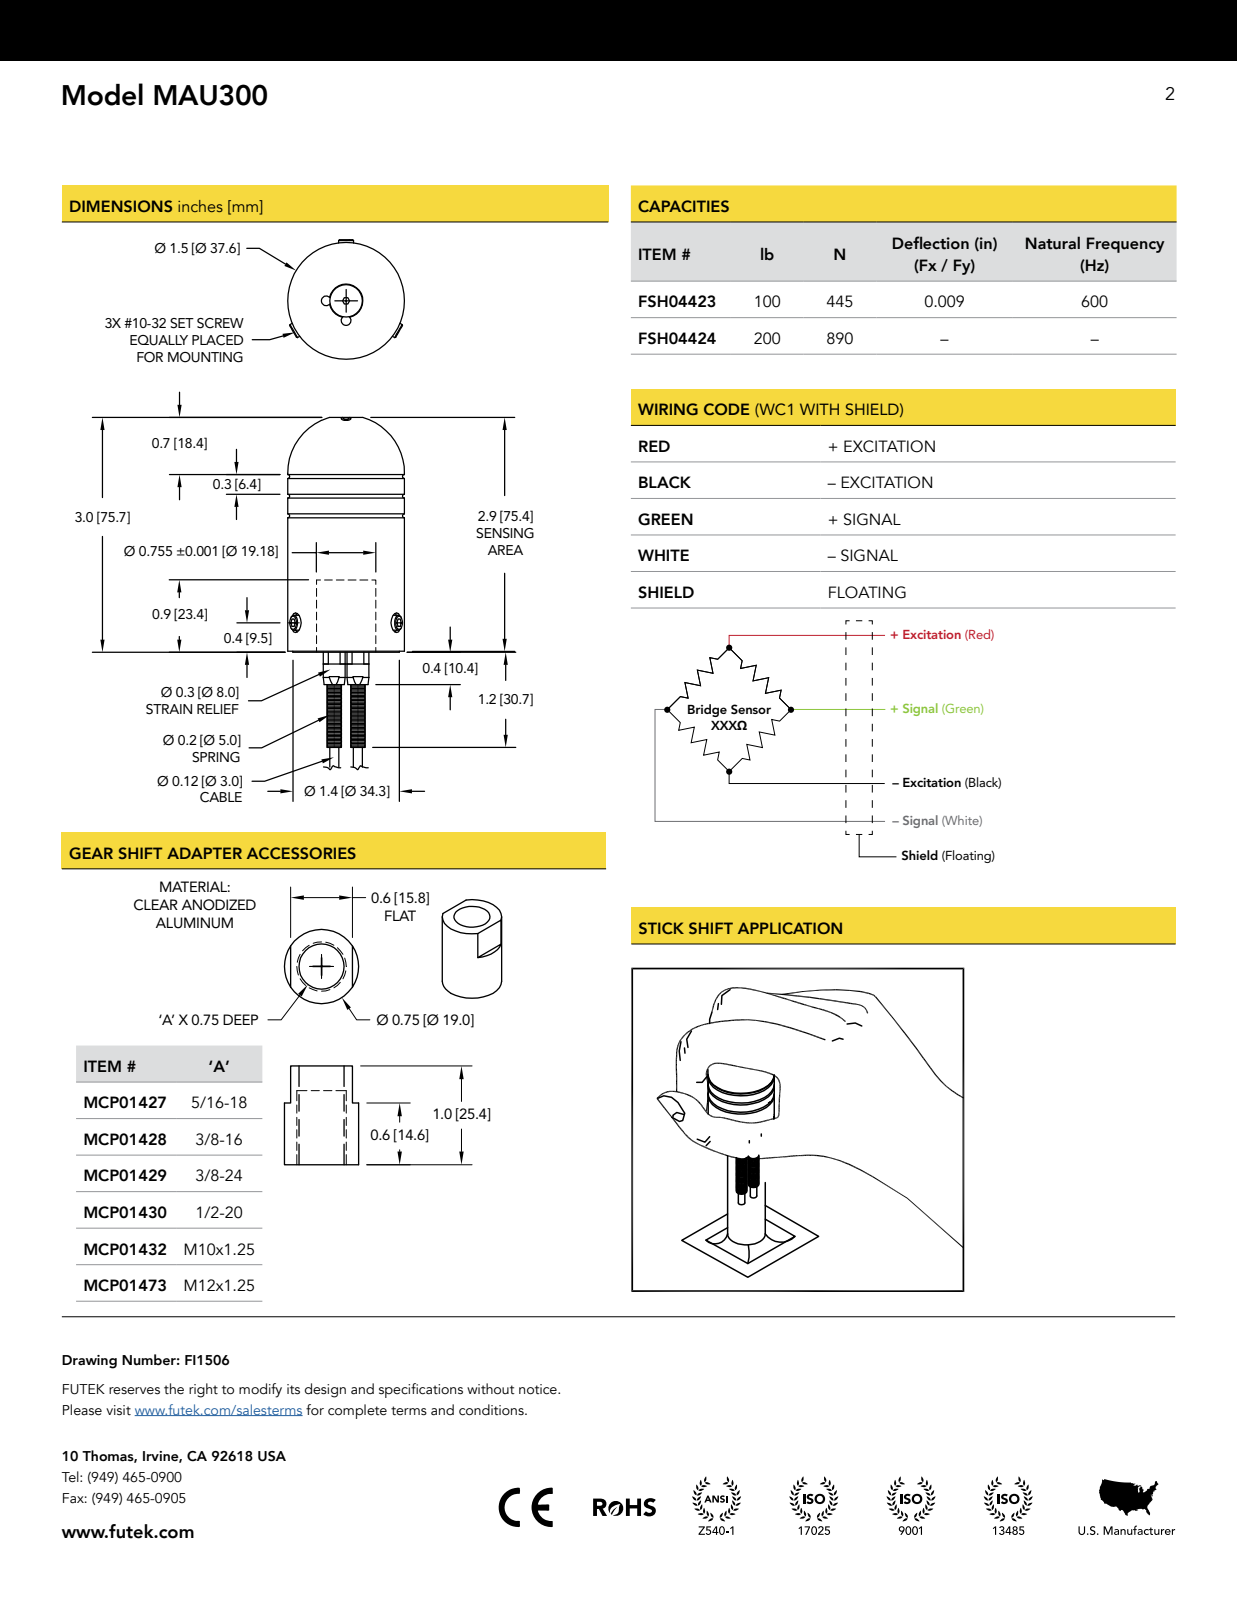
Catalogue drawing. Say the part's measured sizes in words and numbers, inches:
The part is named "FI1035-B (SubstituteLevelofDetail1); FI1035-B_Substitute_1". Its 3-D file was written by "Autodesk Inventor 2011 (AUTOMOTIVE_DESIGN)". It is 3 solids with 421 faces: 150 planar, 107 cylindrical and 164 other. Overall it measures 4.44 by 1.515 by 1.48 inches. Its volume is 3.69 cubic inches and its surface area 41.48 square inches. Round holes: 6 of diameter 0.161, 4 of diameter 0.125, 3 of diameter 0.25, 2 of diameter 0.12, 2 of diameter 0.13, 2 of diameter 0.16, 2 of diameter 0.189, 2 of diameter 0.21, 2 of diameter 0.228, 1 of diameter 0.203, 1 of diameter 0.31, 1 of diameter 0.316. Round bosses or shafts: 4 of diameter 0.19, 2 of diameter 0.278, 2 of diameter 0.225, 2 of diameter 0.205, 2 of diameter 0.115, 1 of diameter 1.48, 1 of diameter 1.35, 1 of diameter 1.16. Partial cylindrical surfaces (rounded edges, fillets, slot ends): 8 of radius 0.1, 2 of radius 0.065, 2 of radius 0.085. The main face-to-face distances are 1.263, 1, 1.213, 0.92, 0.343, 0.263, 0.08, 0.18, 1.1, 0.163. The hole center spacings are 0.25, 0.304, 0.536, 0.3, 0.354, 0.524, 0.652, 1.047.
